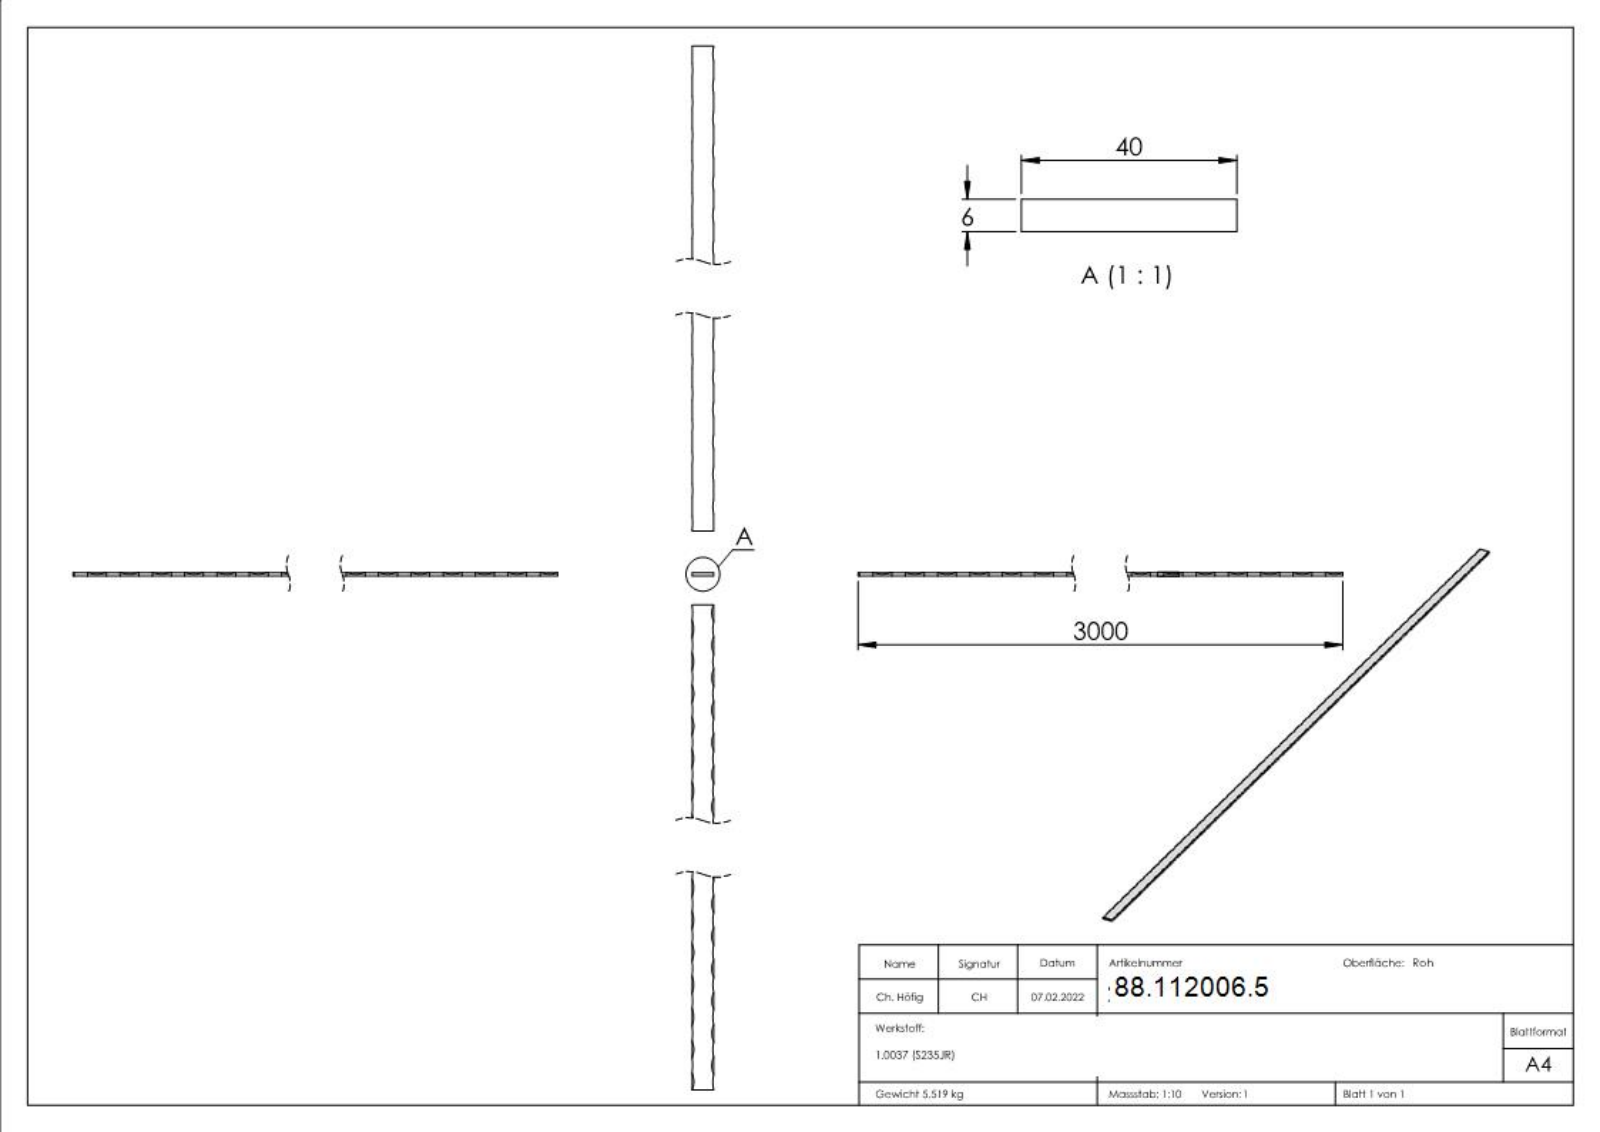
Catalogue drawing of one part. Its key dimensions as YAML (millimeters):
part_name: "2006-5"
step_written_by: "SolidWorks 2018 (CONFIG_CONTROL_DESIGN)"
units: millimeters
bodies: {solids: 1, faces: 562, planar: 236, cylindrical: 100, other: 226}
overall_size: [3000, 40, 6]
volume: 698548
surface_area: 270772
partial_cylinders:
  - {radius: 78.62, count: 100}
face_to_face_distances: [6, 40, 3000, 5.9, 3.27, 0.58, 3.39, 0.34, 20, 1501.01]
